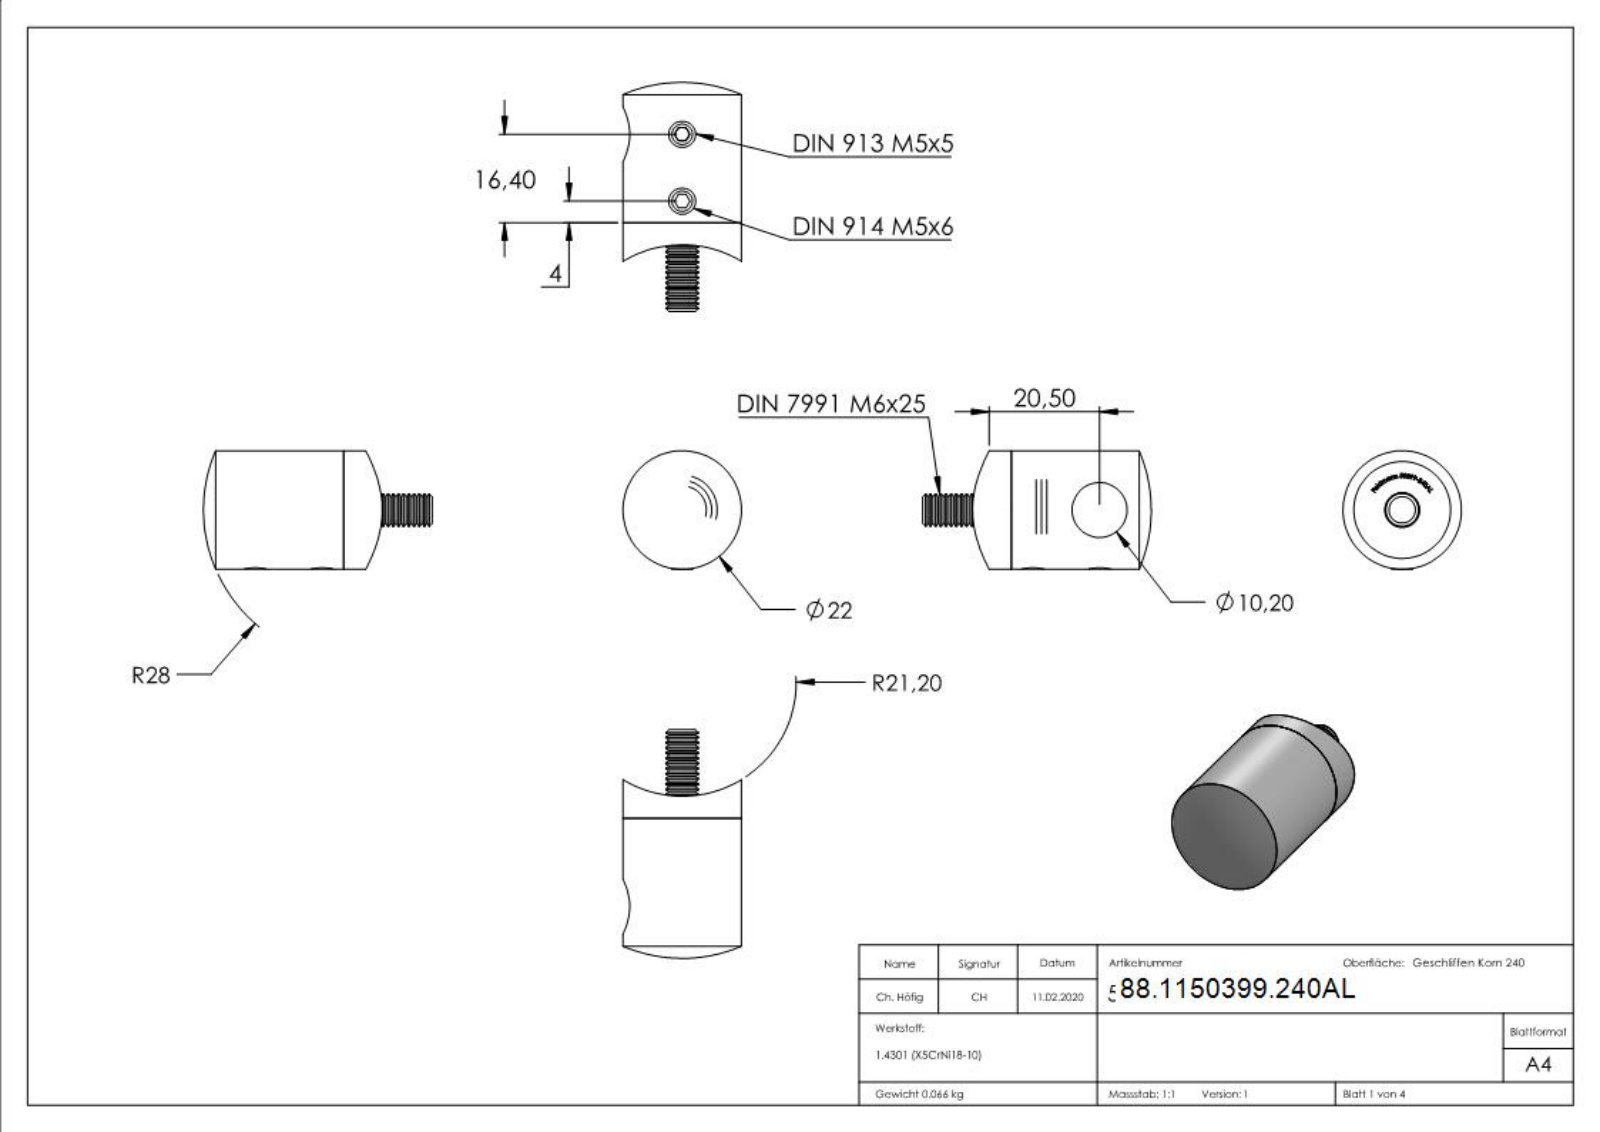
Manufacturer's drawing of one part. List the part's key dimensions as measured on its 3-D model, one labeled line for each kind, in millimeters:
Part name (STEP PRODUCT): socket countersunk head screw_din; 50399-240AL; socket countersunk head screw_din_DIN 7991 - M6 x 25 --- 25S; DIN913_DIN 913 M5x5 (+7 more)
STEP written by: SolidWorks 2015 (CONFIG_CONTROL_DESIGN)
Units: millimetres
Bodies: 5 solids, 388 faces (182 planar, 36 cylindrical, 170 other)
Overall size (bounding box): 70 × 42.45 × 22
Volume: 9 066 mm³ · Surface area: 6 162 mm²
Round holes (diameter × count): ⌀4.2 ×2, ⌀6.5 ×1, ⌀10.2 ×1, ⌀12 ×1, ⌀18 ×1
Round bosses / shafts (diameter × count): ⌀5 ×2, ⌀22 ×1, ⌀11.9 ×1, ⌀11.57 ×1, ⌀6 ×1
Partial cylindrical surfaces — rounded edges, fillets, slot ends (radius × count): R21.2 ×1
Main face-to-face distances: 2.1, 10.65, 8.55, 2.5, 9.6, 7.5, 1.05, 14.35, 16.45, 23.95
Hole centre spacings: 12.4
